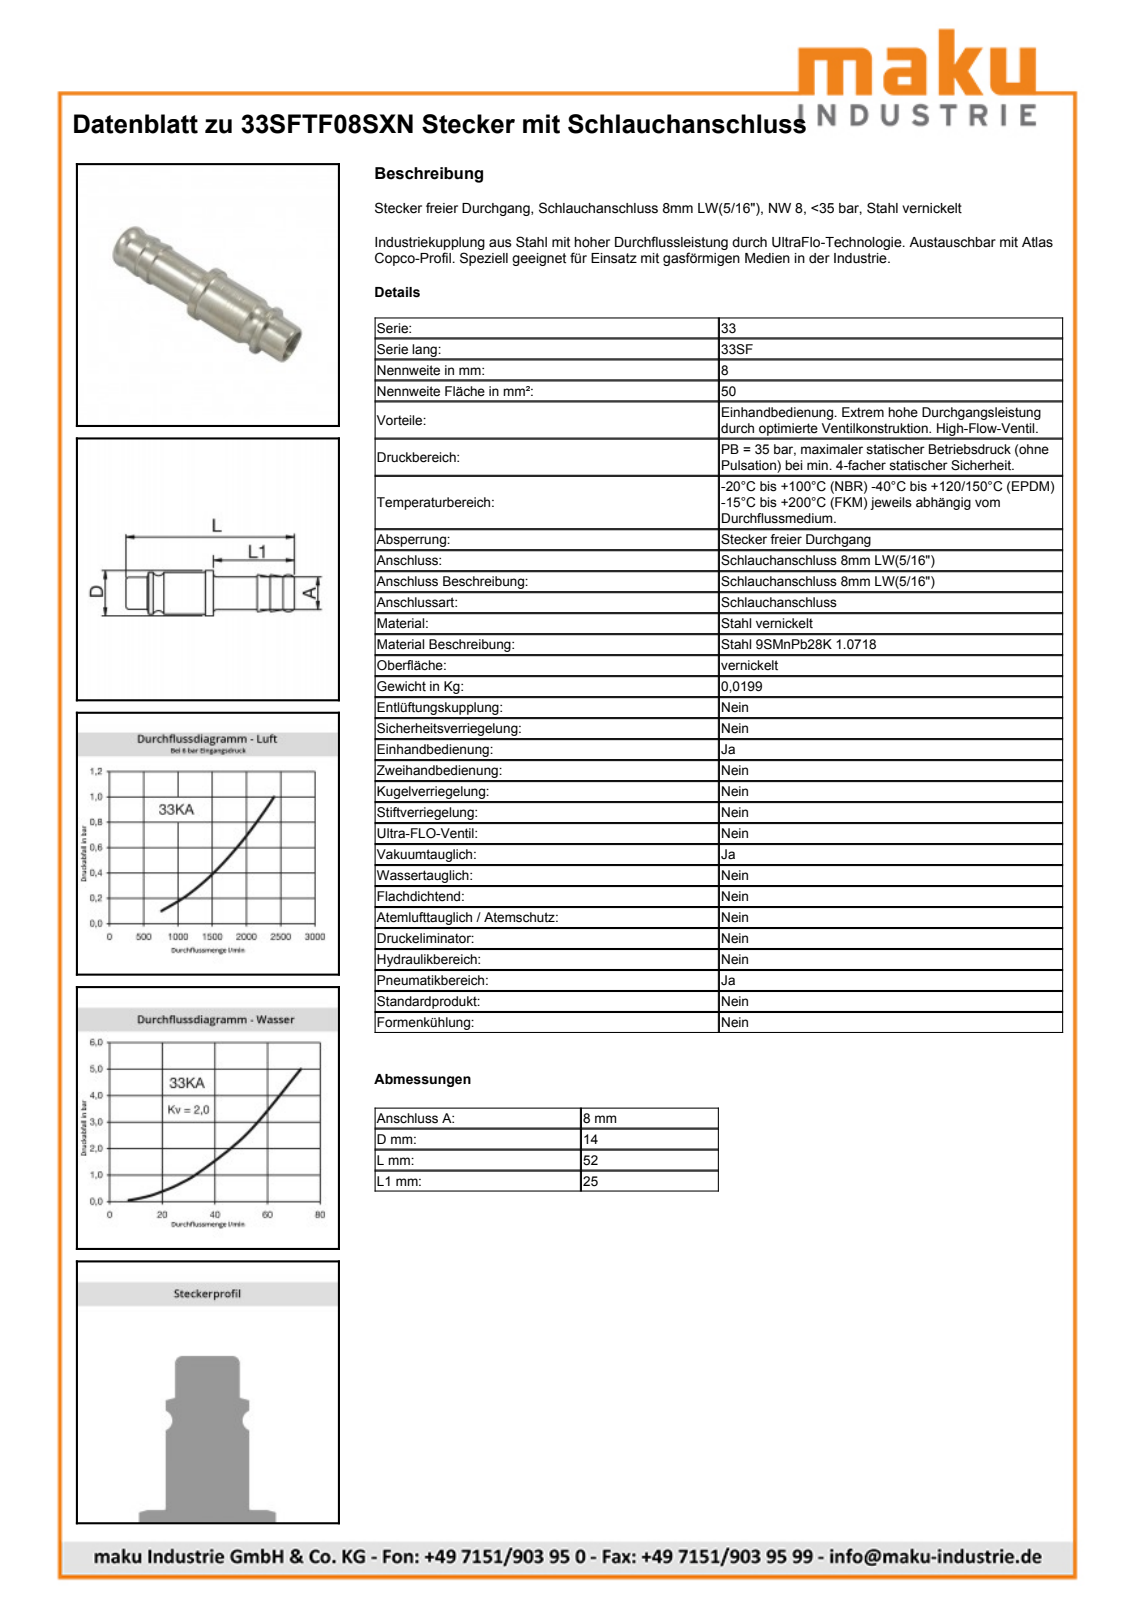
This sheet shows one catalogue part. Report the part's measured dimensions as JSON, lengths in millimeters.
{"part_name": "D107393", "step_written_by": "Autodesk Inventor 2013 (AUTOMOTIVE_DESIGN)", "units": "millimeters", "bodies": {"solids": 1, "faces": 27, "planar": 6, "cylindrical": 7, "other": 14}, "overall_size": [52, 14, 14], "volume_mm3": 2568, "surface_area_mm2": 3069, "round_holes": [[6, 1], [7.8, 1]], "round_bosses_or_shafts": [[14, 1], [12.9, 1], [9.9, 1], [8.1, 1]], "face_to_face_distances": [25, 11.5, 13.5, 27.5, 16, 2.5, 52, 40.5, 27, 24.5]}
